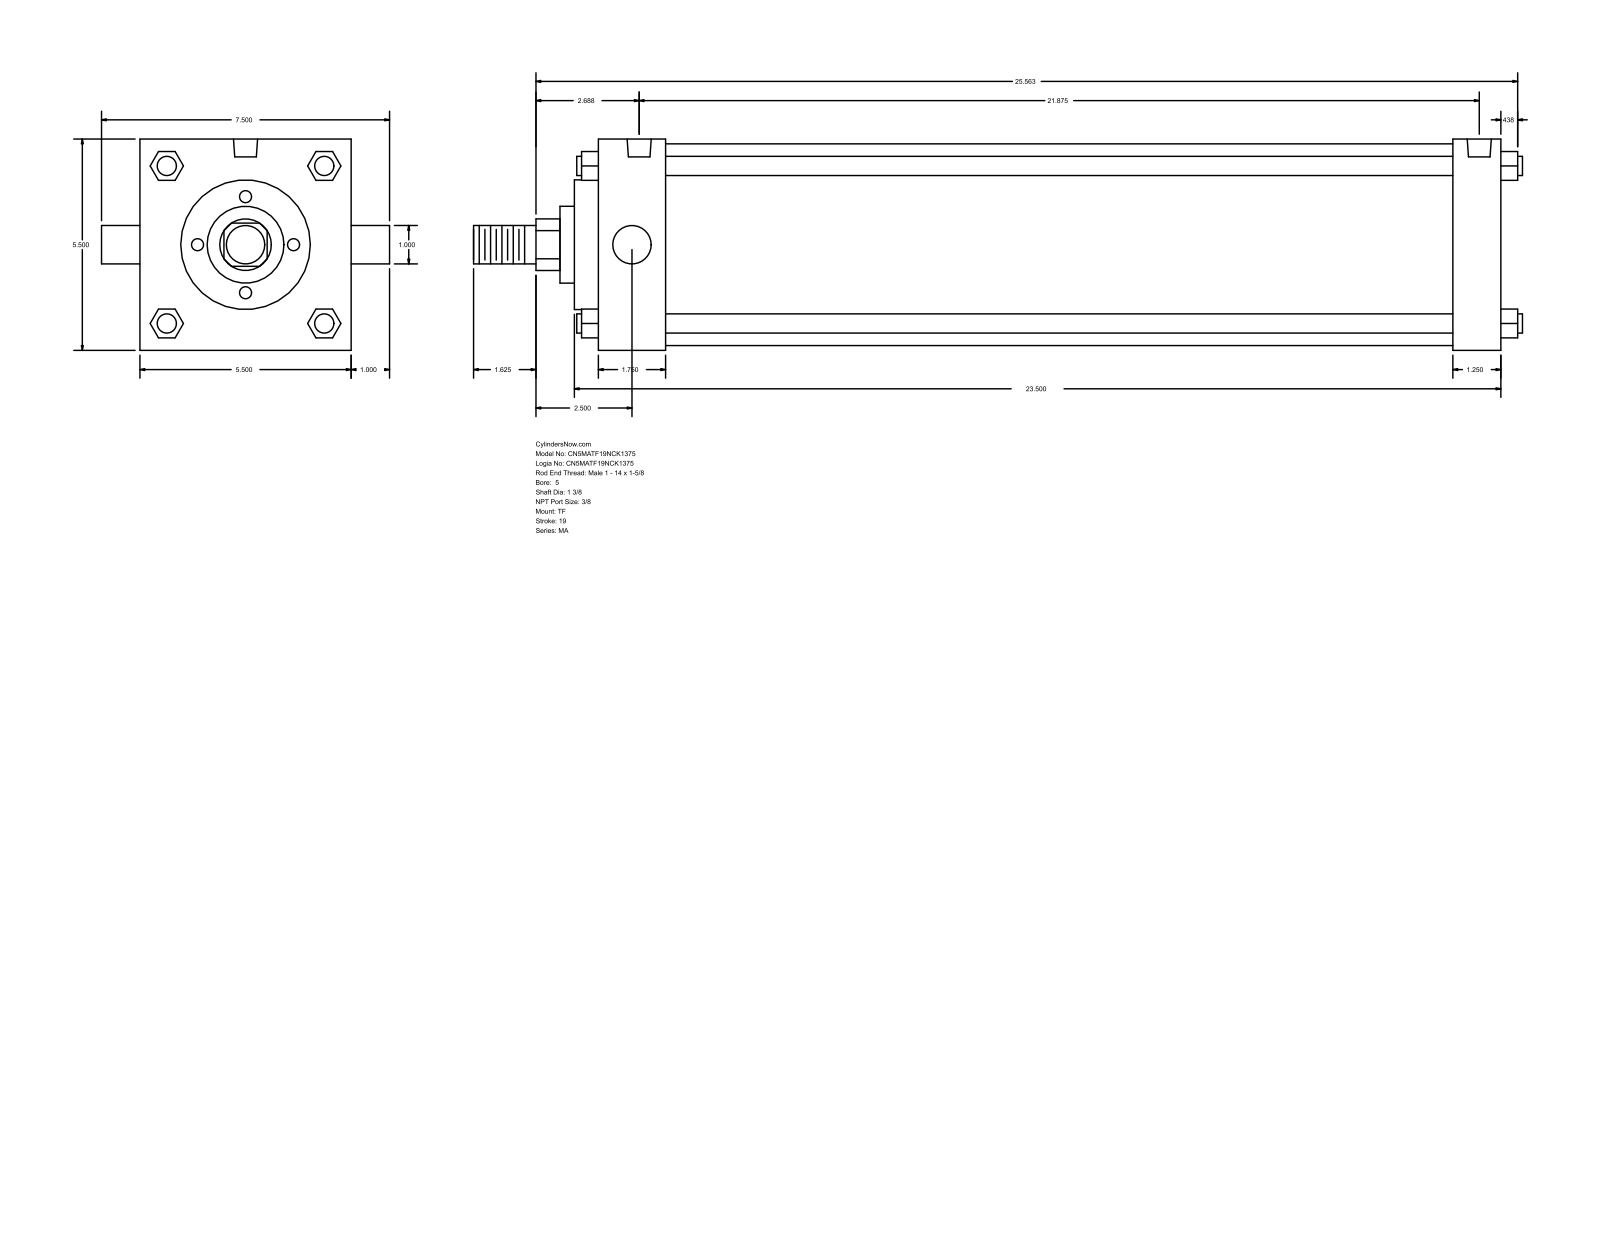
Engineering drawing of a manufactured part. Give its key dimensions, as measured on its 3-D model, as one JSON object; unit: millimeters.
{"part_name": "MA_TF__0500_1.375", "step_written_by": "GSSL Pune (CONFIG_CONTROL_DESIGN)", "units": "millimeters", "bodies": {"solids": 0, "faces": 122, "planar": 93, "cylindrical": 29, "other": 0}, "overall_size": [693.74, 190.5, 139.7], "round_holes": [[11.11, 3], [15.93, 2]], "round_bosses_or_shafts": [[12.7, 4], [25.4, 2], [133.35, 1], [85.72, 1], [50.8, 1], [34.92, 1]], "partial_cylinders_radius": [[17.06, 1]], "face_to_face_distances": [139.7, 596.9, 565.15, 31.75, 44.45, 520.7, 552.45, 15.87, 60.32, 581.02], "hole_center_spacings": [4.77, 550.86, 546.09, 555.63]}
